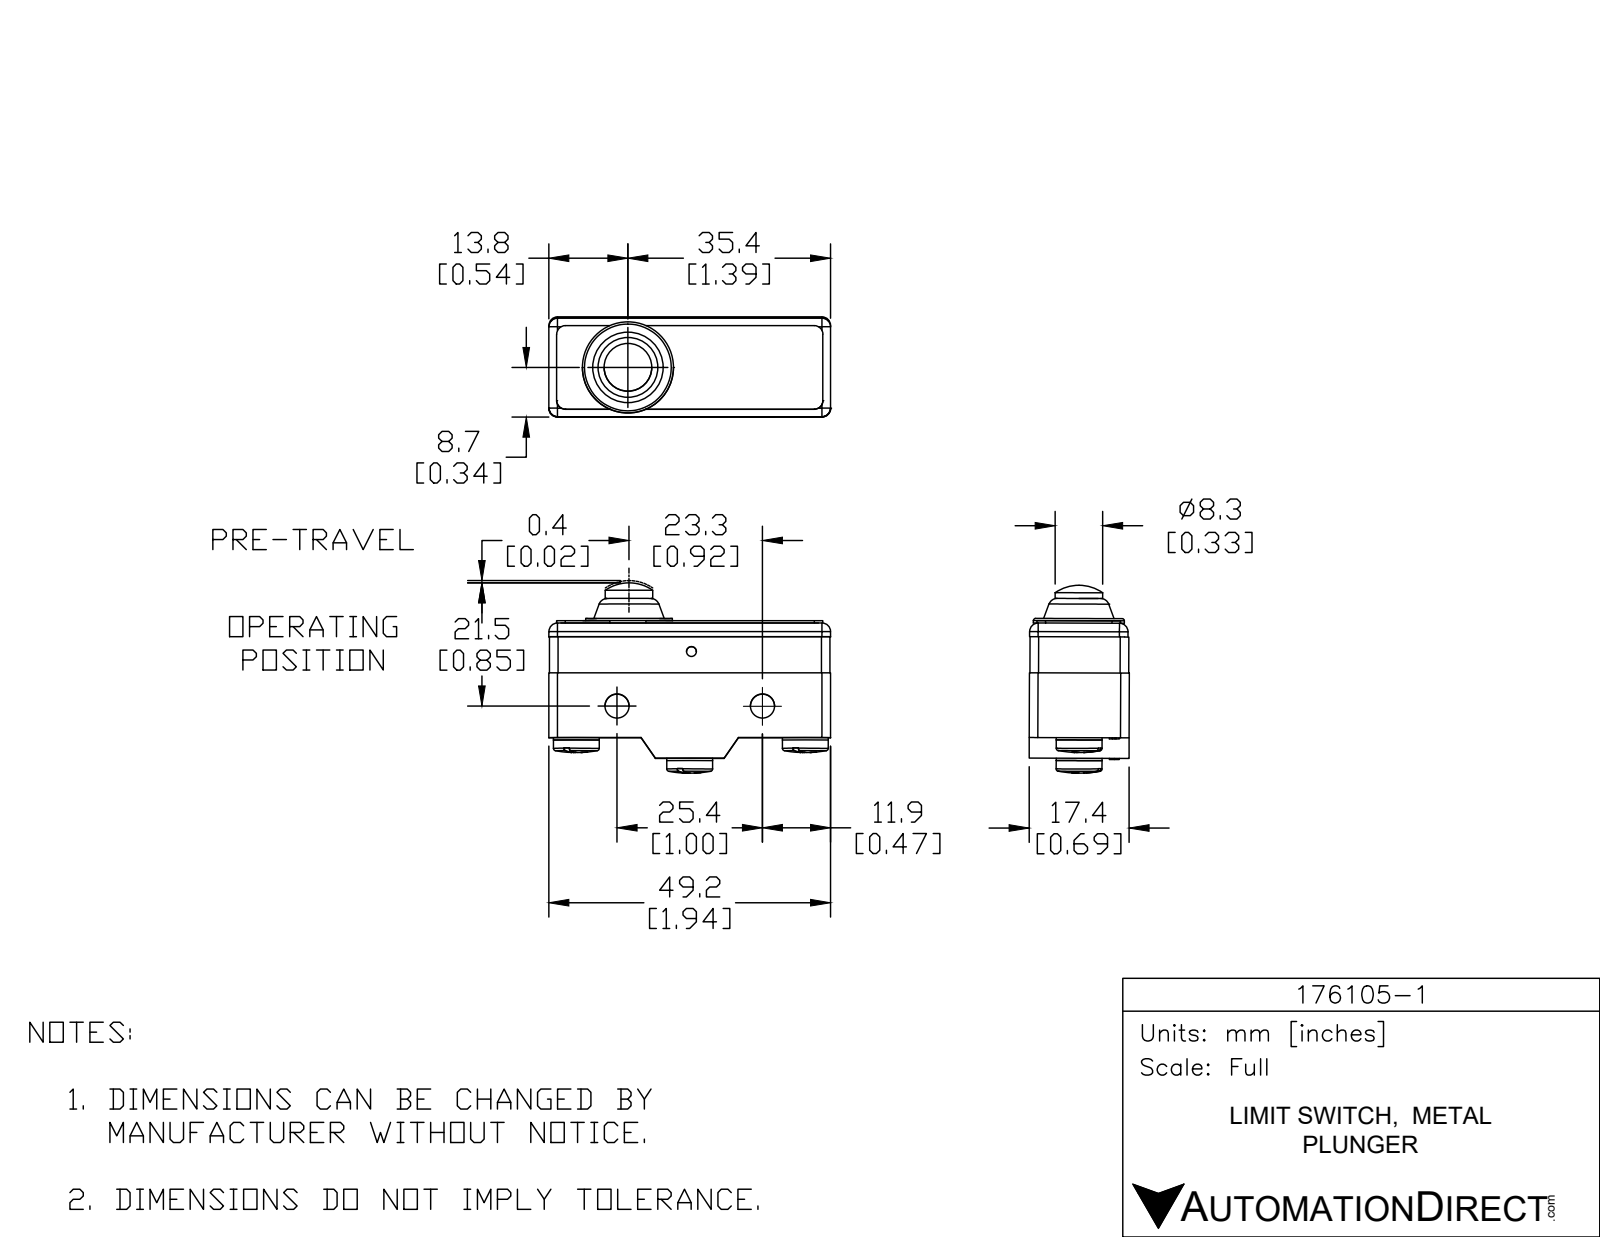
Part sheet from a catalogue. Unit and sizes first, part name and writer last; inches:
Units: inches
Overall size (bounding box): 1.937 × 1.291 × 0.689
Round holes (diameter × count): ⌀0.15 ×3, ⌀0.236 ×3, ⌀0.165 ×2, ⌀0.067 ×1, ⌀0.295 ×1
Round bosses / shafts (diameter × count): ⌀0.315 ×3, ⌀0.626 ×1, ⌀0.327 ×1
Partial cylindrical surfaces — rounded edges, fillets, slot ends (radius × count): R0.059 ×18, R0.012 ×12, R0.116 ×3
Main face-to-face distances: 0.683, 0.693, 0.687, 0.803, 0.11, 0.016, 0.142, 0.679, 0.835, 0.945
Hole centre spacings: 0.354, 0.425, 0.615, 0.634, 0.78, 0.795, 1, 1.22
Volume: 1.053 in³ · Surface area: 13.05 in²
Bodies: 9 solids, 470 faces (203 planar, 111 cylindrical, 156 other)
Part name (STEP PRODUCT): 176-MS (Screw Terminal)-Short Spring Plunger
STEP written by: SolidWorks 2018 (AUTOMOTIVE_DESIGN)
